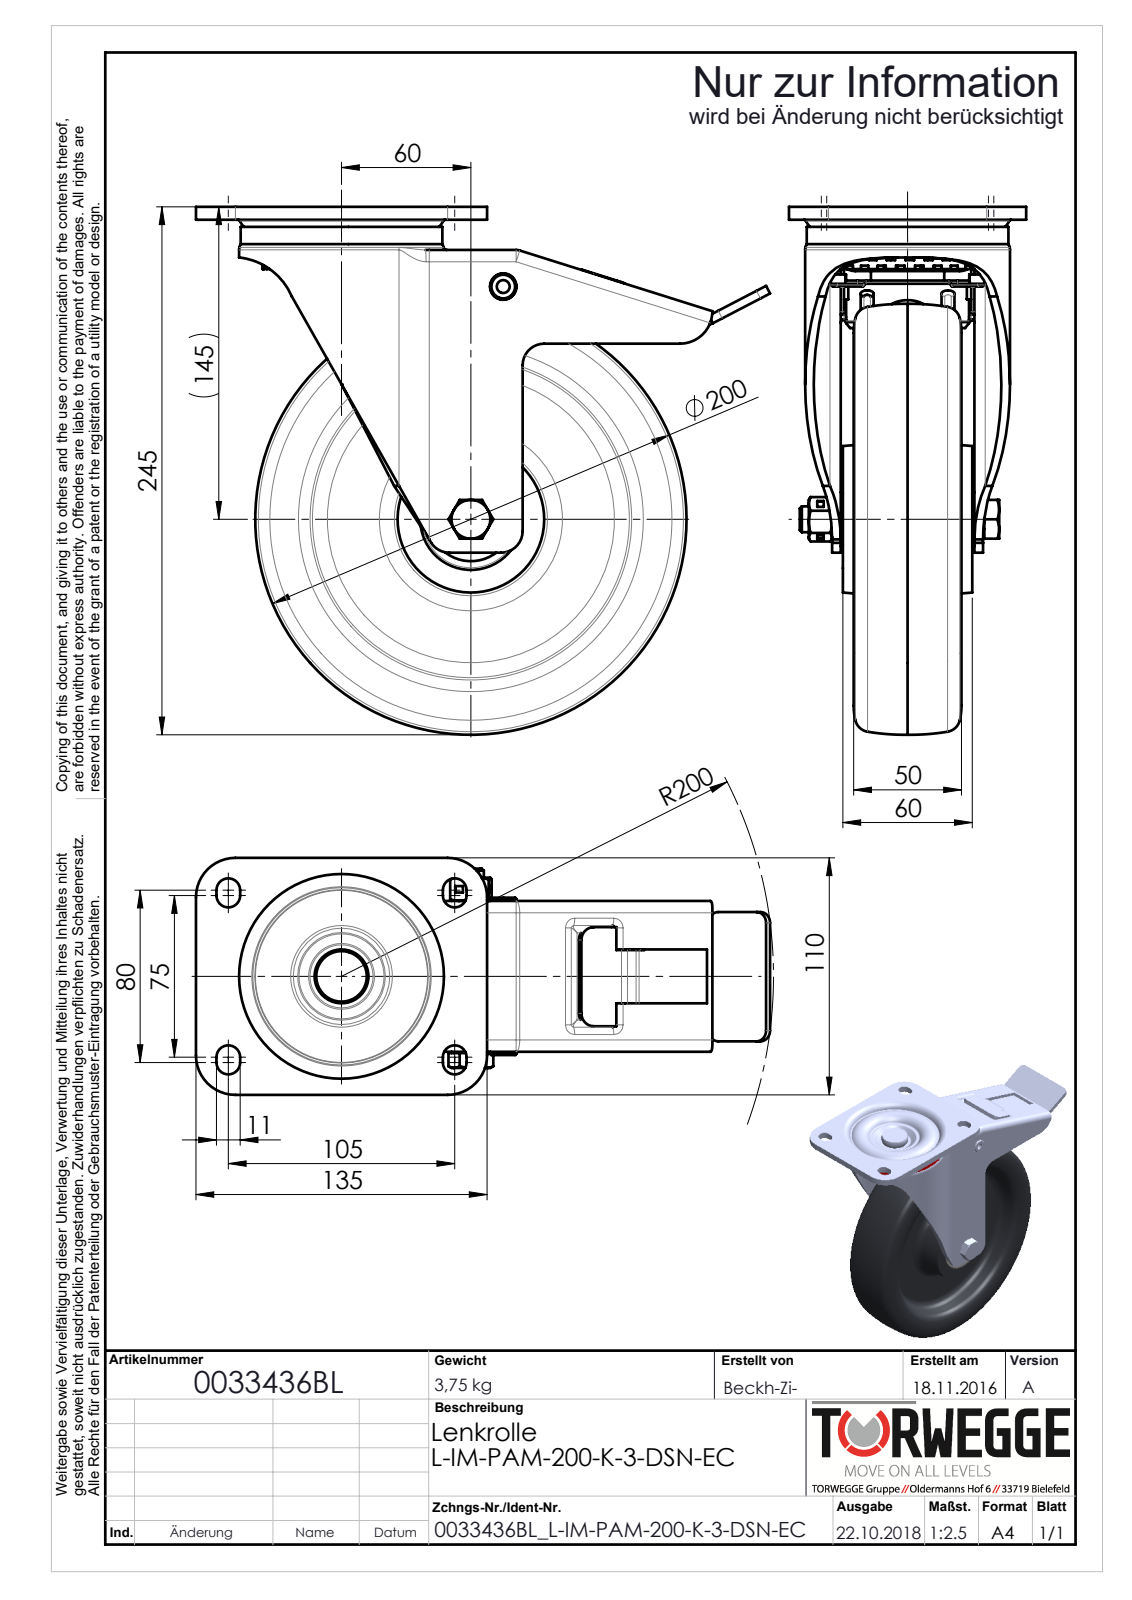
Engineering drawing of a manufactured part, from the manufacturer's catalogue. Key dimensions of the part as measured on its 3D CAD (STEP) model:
Part name (STEP PRODUCT): 0033436BL_L-IM-PAM-200-K-3-DSN-EC
STEP written by: SolidWorks 2016 (AUTOMOTIVE_DESIGN)
Units: millimetres
Bodies: 21 solids, 1453 faces (782 planar, 366 cylindrical, 305 other)
Overall size (bounding box): 266.25 × 245 × 110
Volume: 1 372 000 mm³ · Surface area: 336 509 mm²
Round holes (diameter × count): ⌀16.2 ×2, ⌀3.6 ×1, ⌀6 ×1, ⌀6.6 ×1, ⌀8 ×1, ⌀9.6 ×1, ⌀10.2 ×1, ⌀11 ×1, ⌀12 ×1, ⌀12.2 ×1, ⌀12.3 ×1, ⌀12.6 ×1
Round bosses / shafts (diameter × count): ⌀18 ×3, ⌀8 ×2, ⌀93.54 ×1, ⌀73.32 ×1, ⌀47 ×1, ⌀28.1 ×1, ⌀25 ×1, ⌀24 ×1
Partial cylindrical surfaces — rounded edges, fillets, slot ends (radius × count): R1.5 ×15, R3 ×13, R5.5 ×13, R4 ×12, R5 ×11, R0.31 ×8, R0.75 ×8, R0.17 ×7
Main face-to-face distances: 4, 25.5, 36.5, 29.5, 40.5, 66, 1.5, 11, 1, 62
Hole centre spacings: 109.04
